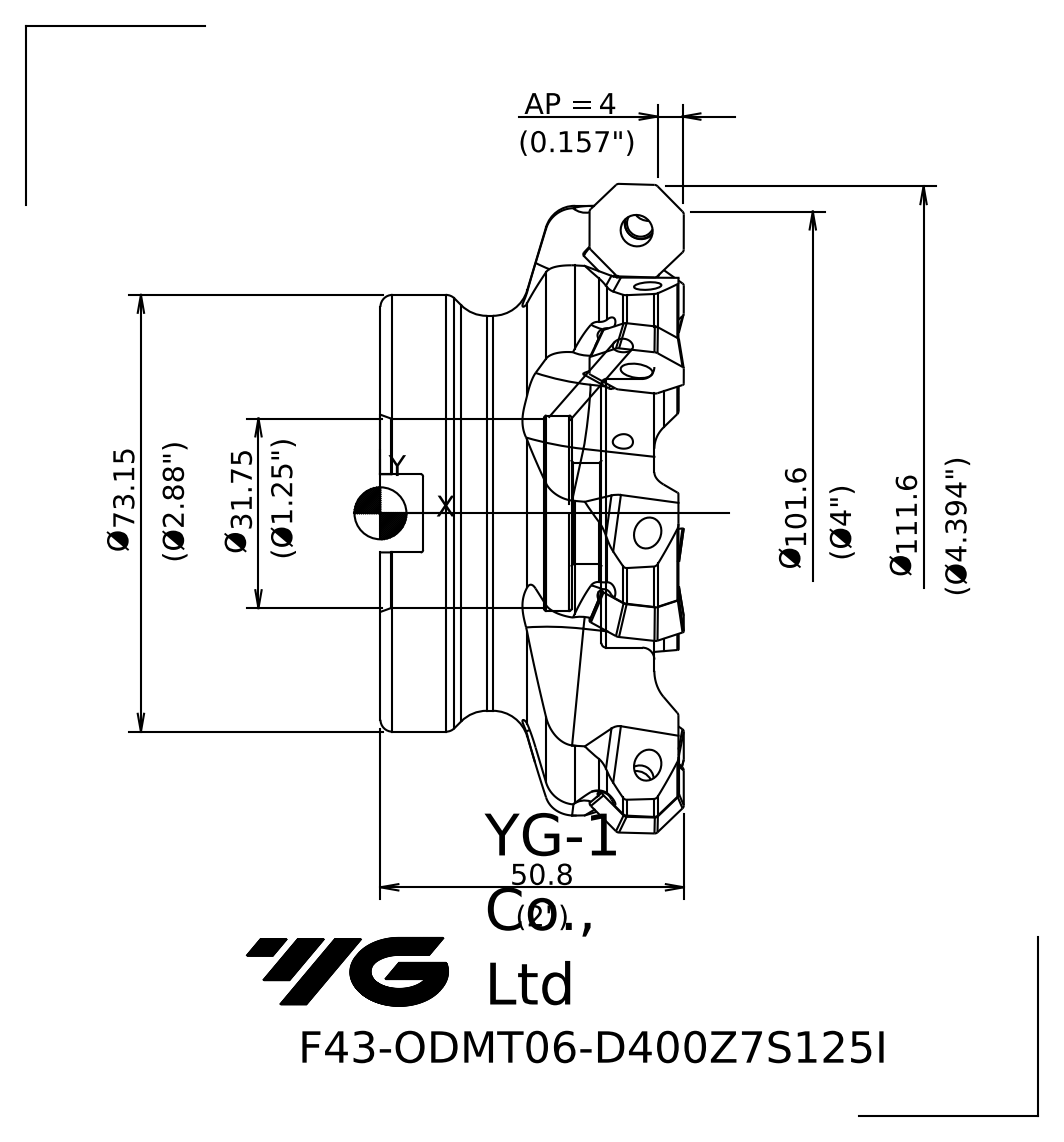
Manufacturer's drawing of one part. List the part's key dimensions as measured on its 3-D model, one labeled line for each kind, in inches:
Part name (STEP PRODUCT): 102241DCD294w9vs
STEP written by: SIEMENS PLM Software NX 10.0 (AP203_CONFIGURATION_CONTROLLED_3D_DESIGN_OF_MECHANICAL_PARTS_AND_ASSEMBLIES_MIM_LF)
Units: inches
Bodies: 1 solid, 66 faces (12 planar, 12 cylindrical, 42 other)
Overall size (bounding box): 4.397 × 4.397 × 2
Volume: 14.52 in³ · Surface area: 78.21 in²
Round holes (diameter × count): ⌀0.669 ×1, ⌀1.25 ×1, ⌀1.289 ×1, ⌀1.772 ×1
Round bosses / shafts (diameter × count): ⌀4.316 ×1, ⌀4.054 ×1, ⌀2.88 ×1, ⌀2.604 ×1
Partial cylindrical surfaces — rounded edges, fillets, slot ends (radius × count): R0.016 ×2
Main face-to-face distances: 1.806, 0.349, 1.457, 0.546, 0.197, 1.26, 1.525, 1.176, 0.979, 0.281
